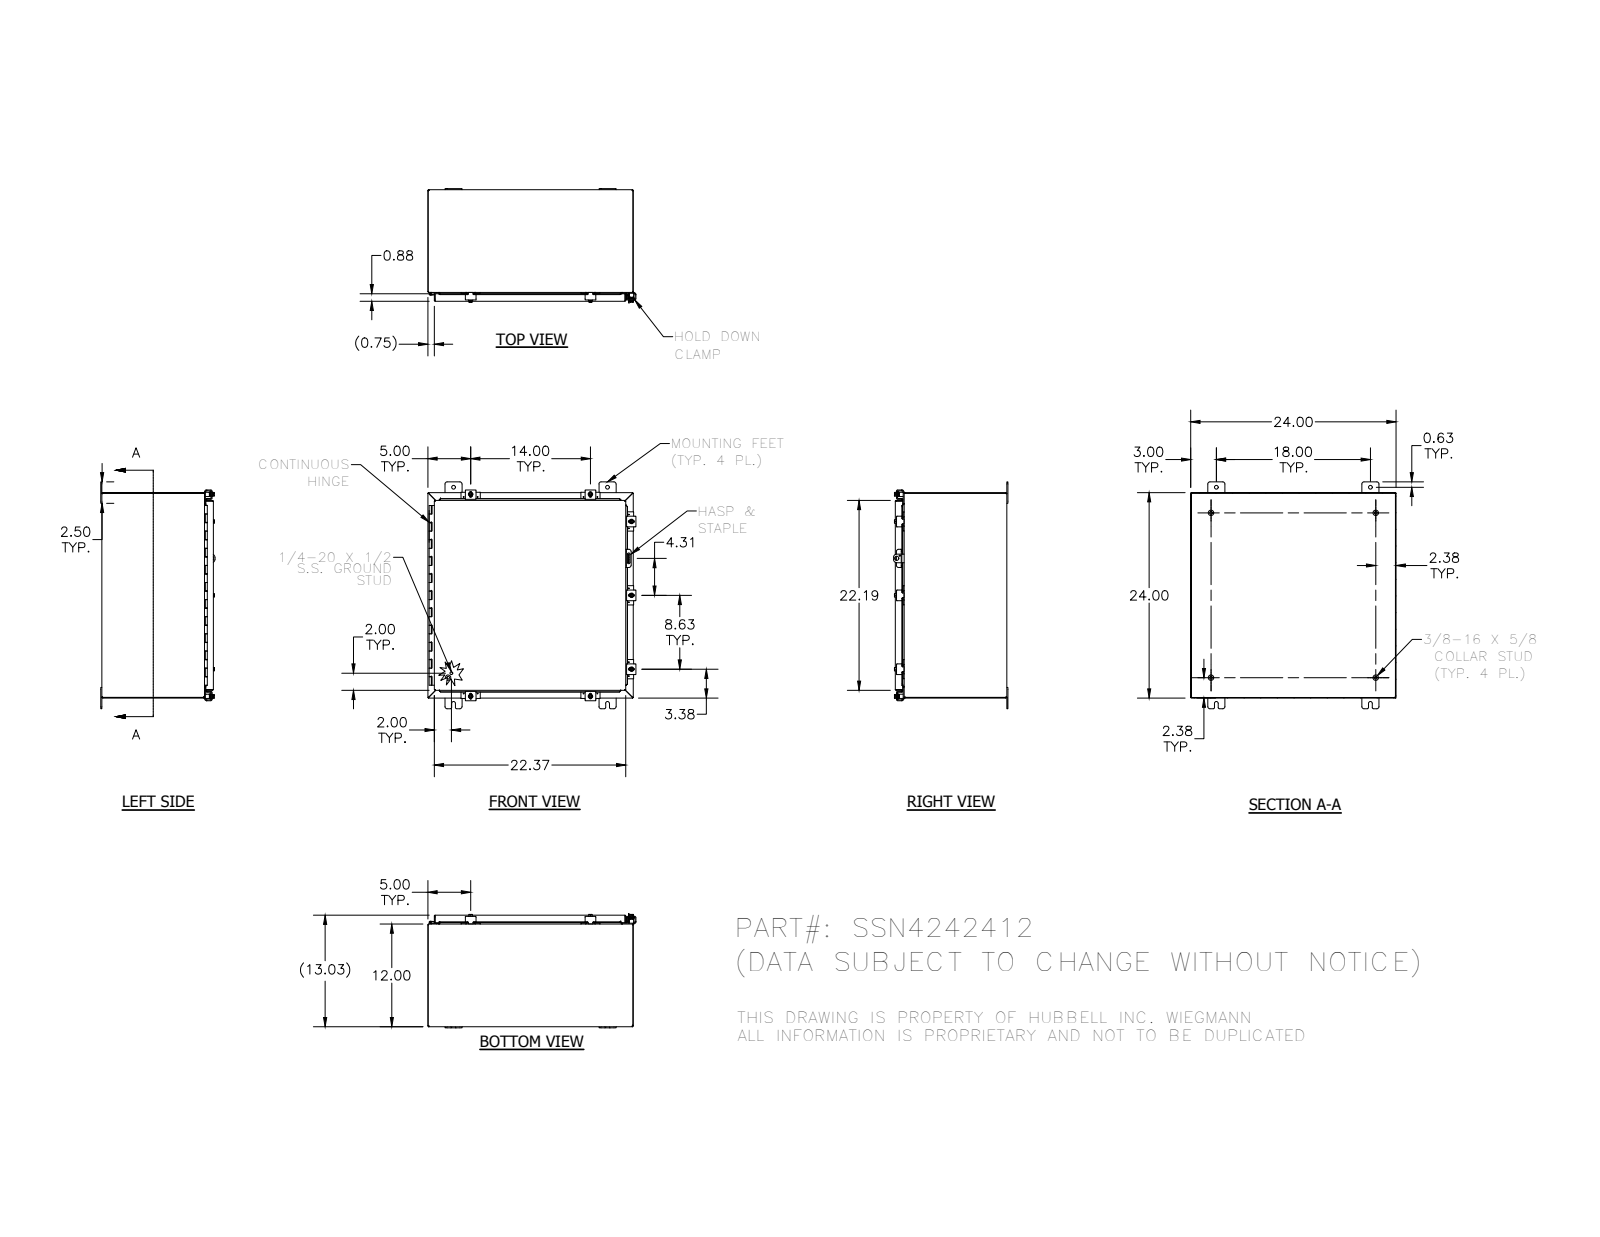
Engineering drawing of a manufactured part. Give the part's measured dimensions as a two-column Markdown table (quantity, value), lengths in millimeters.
| quantity | value |
| --- | --- |
| part name | SSN4242412; HFW30825-3; 328138T; 34871 (+8 more) |
| STEP written by | SolidWorks 2014 (AUTOMOTIVE_DESIGN) |
| units | millimeters |
| bodies | 52 solids, 2042 faces (772 planar, 899 cylindrical, 371 other) |
| overall size | 673.1 × 617.5 × 339.2 |
| volume | 3 340 000 mm³ |
| surface area | 3 464 000 mm² |
| round holes (diameter × count) | 2.8 × 14, 5.4 × 7, 7.1 × 7, 7.6 × 7, 11.1 × 4, 3.2 × 1, 4 × 1, 12.7 × 1 |
| round bosses / shafts (diameter × count) | 6.4 × 9, 13.2 × 7, 12.7 × 7, 8.9 × 7, 15.9 × 4, 8.4 × 4, 2.9 × 2, 8.6 × 1 |
| partial cylindrical surfaces (radius × count) | 0.8 × 83, 3.2 × 37, 6.4 × 33, 0.8 × 23, 2.7 × 23, 1.6 × 15, 3.6 × 14, 2.5 × 10 |
| main face-to-face distances | 1.9, 607.7, 329.2, 605.8, 609.6, 327.3, 331, 302.9, 26.2, 304.8 |
| hole center spacings | 22.3, 591.9, 355.6, 41.3, 335.1, 376.3, 498.8, 583.2 |
